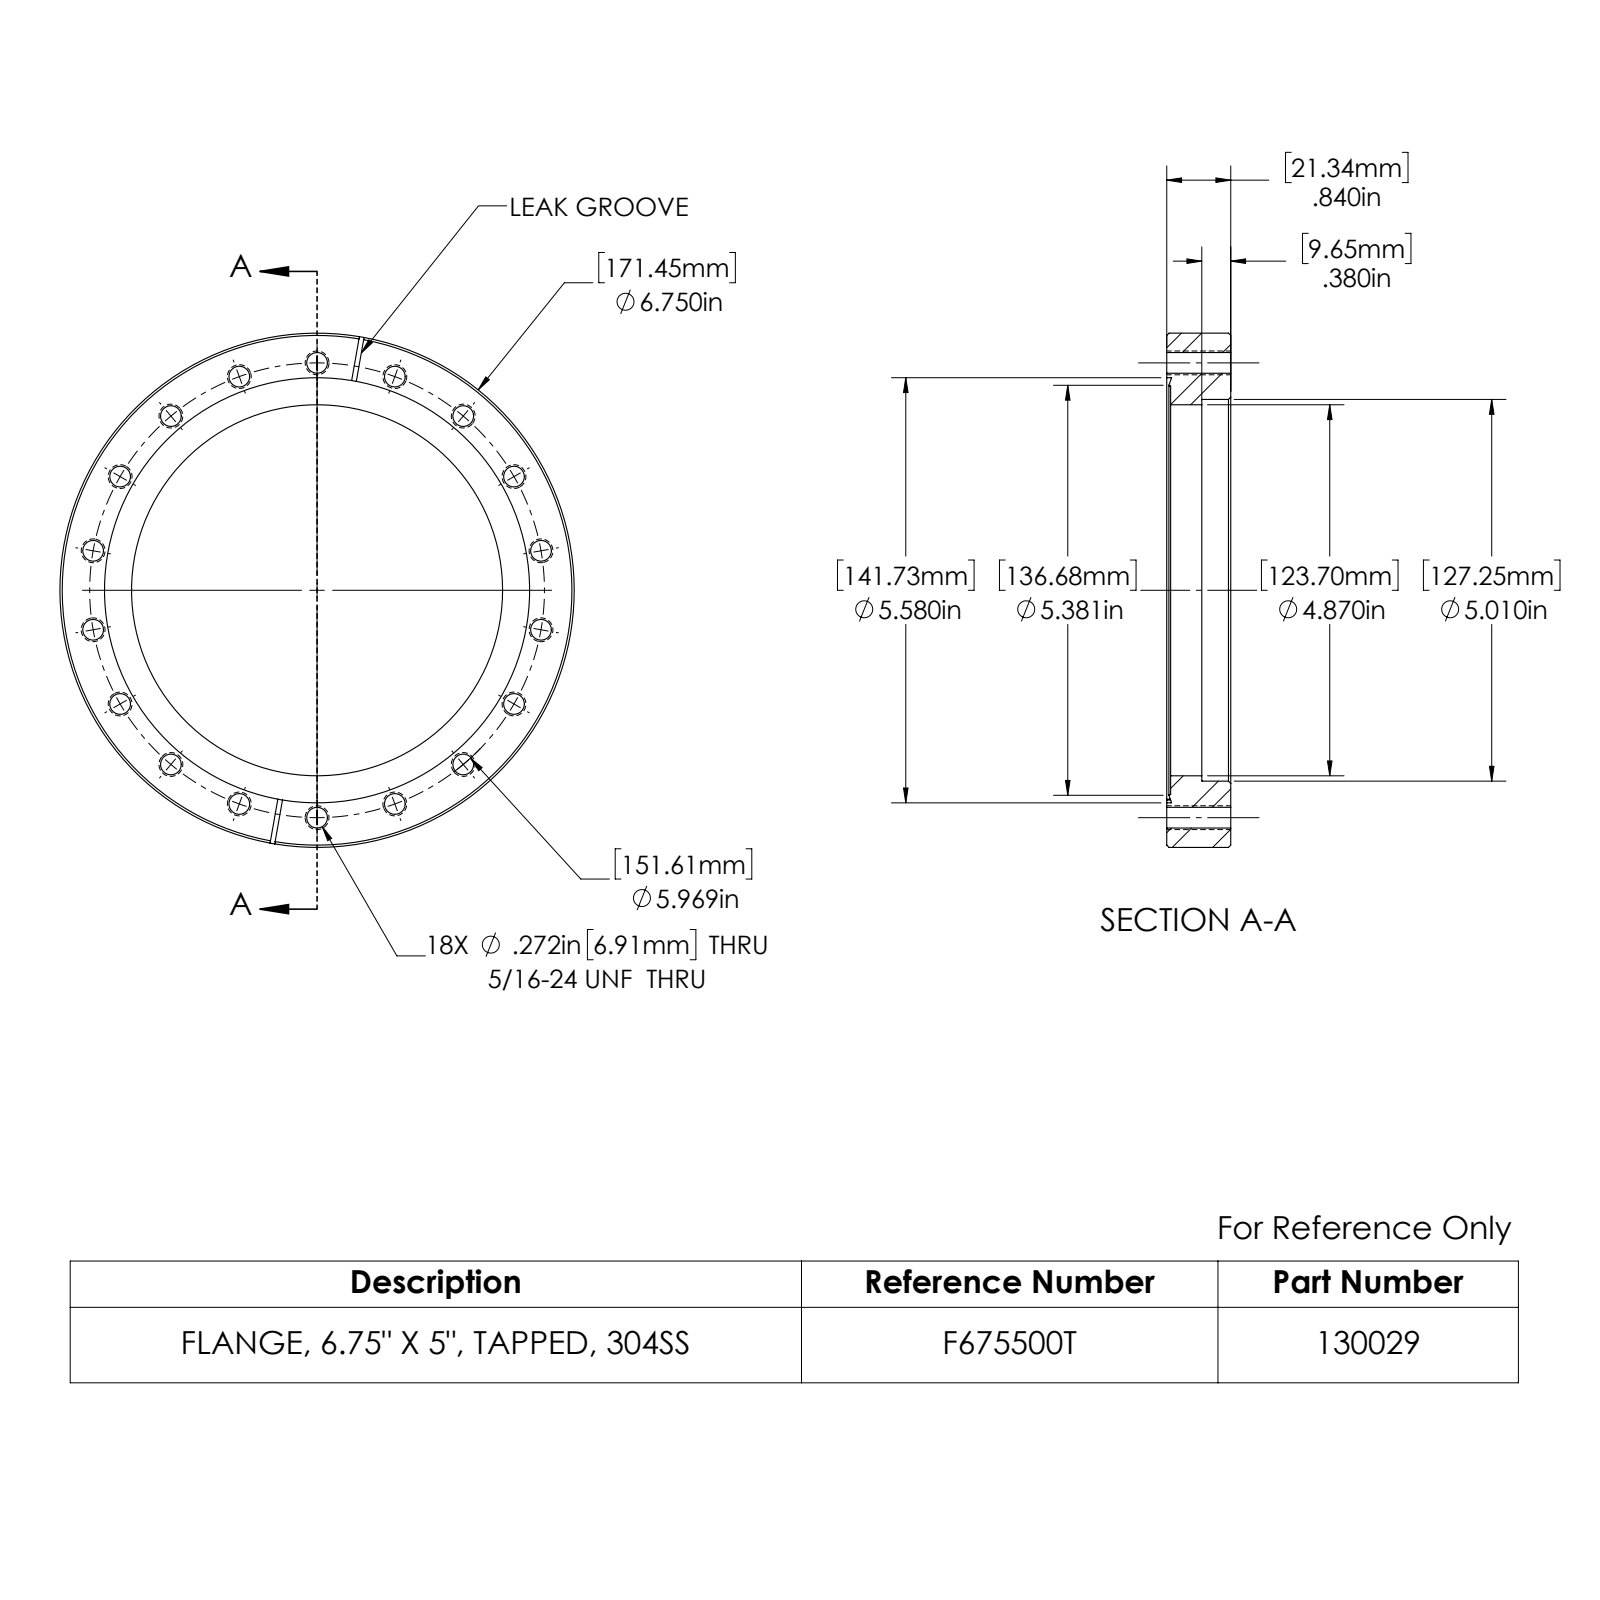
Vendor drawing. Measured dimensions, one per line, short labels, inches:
name: 130029_E
written by: SolidWorks 2022 (CONFIG_CONTROL_DESIGN)
unit: in
bodies: 1 solid, 74 faces (11 planar, 44 cylindrical, 19 other)
size: 6.75 × 6.75 × 0.84
volume: 12.81 in³; area: 75.68 in²
holes: 18× ⌀0.272, 1× ⌀4.87, 1× ⌀5.01, 1× ⌀5.58
bosses: 1× ⌀6.75
face distances: 0.84, 0.051, 0.789, 0.46, 0.409, 0.38, 0.052, 0.408, 0.788, 0.06
hole spacings: 2.984, 1.037, 2.985, 4.572, 2.041, 5.878, 3.837, 5.169
